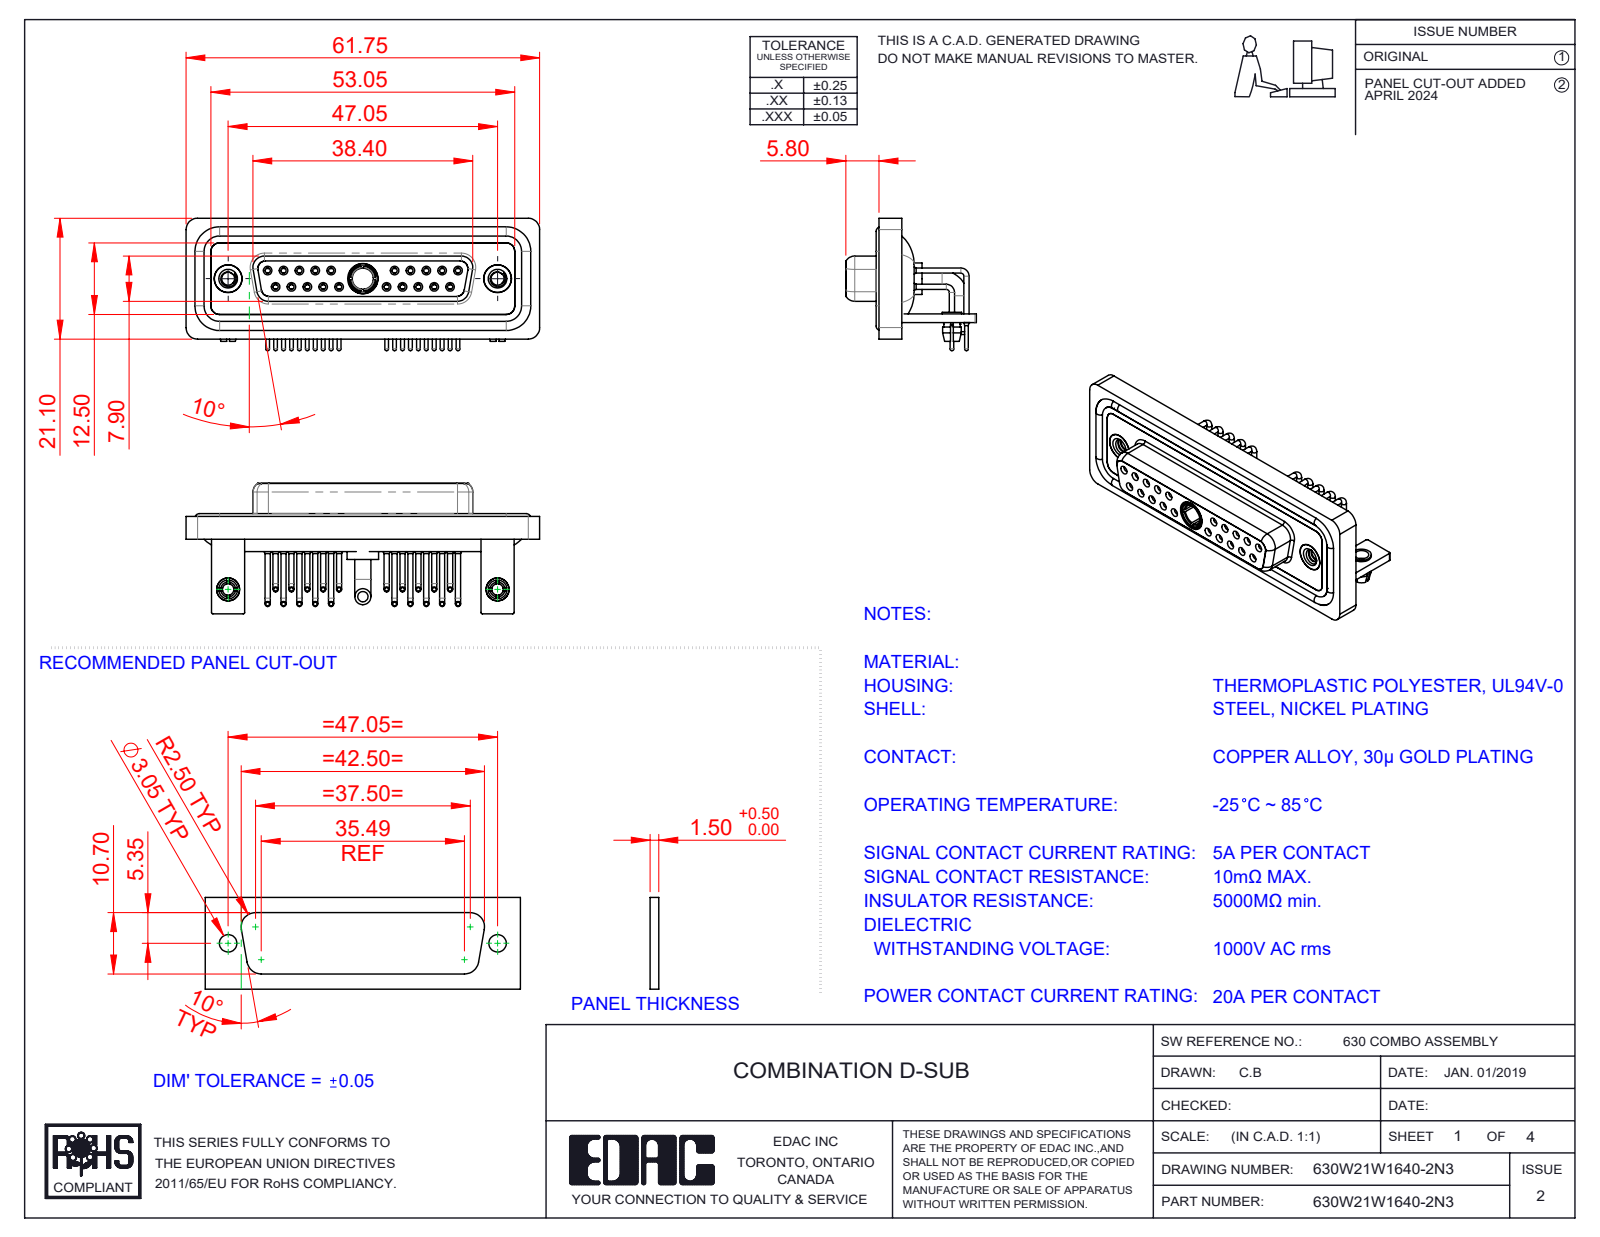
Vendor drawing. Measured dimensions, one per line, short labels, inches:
name: 630Combo Threaded Rivet_2; 630Combo Contact Row 2_50 Contacts; 630Combo Board Lock_50 Contacts; 630Combo Contact Row 1_50 Contacts (+7 more)
written by: SolidWorks 2023 (CONFIG_CONTROL_DESIGN)
unit: in
bodies: 33 solids, 1664 faces (502 planar, 729 cylindrical, 433 other)
size: 2.431 × 0.91 × 0.898
volume: 0.544 in³; area: 24.37 in²
holes: 22× ⌀0.079, 20× ⌀0.035, 20× ⌀0.043, 20× ⌀0.059, 10× ⌀0.063, 10× ⌀0.067, 3× ⌀0.191, 2× ⌀0.089, 2× ⌀0.098, 2× ⌀0.126, 2× ⌀0.157, 2× ⌀0.159
bosses: 20× ⌀0.035, 20× ⌀0.026, 14× ⌀0.063, 2× ⌀0.195, 2× ⌀0.189, 2× ⌀0.157, 2× ⌀0.134, 2× ⌀0.13
rounds: 19× R0.079, 18× R0.059, 16× R0.01, 8× R0.053, 8× R0.063, 5× R0.02, 4× R0.024, 4× R0.026
face distances: 0.016, 0.071, 0.114, 0.146, 0.059, 0.161, 0.043, 0.055, 0.063, 0.098
hole spacings: 0.124, 0.109, 0.218, 0.327, 0.198, 0.763, 0.826, 0.872
